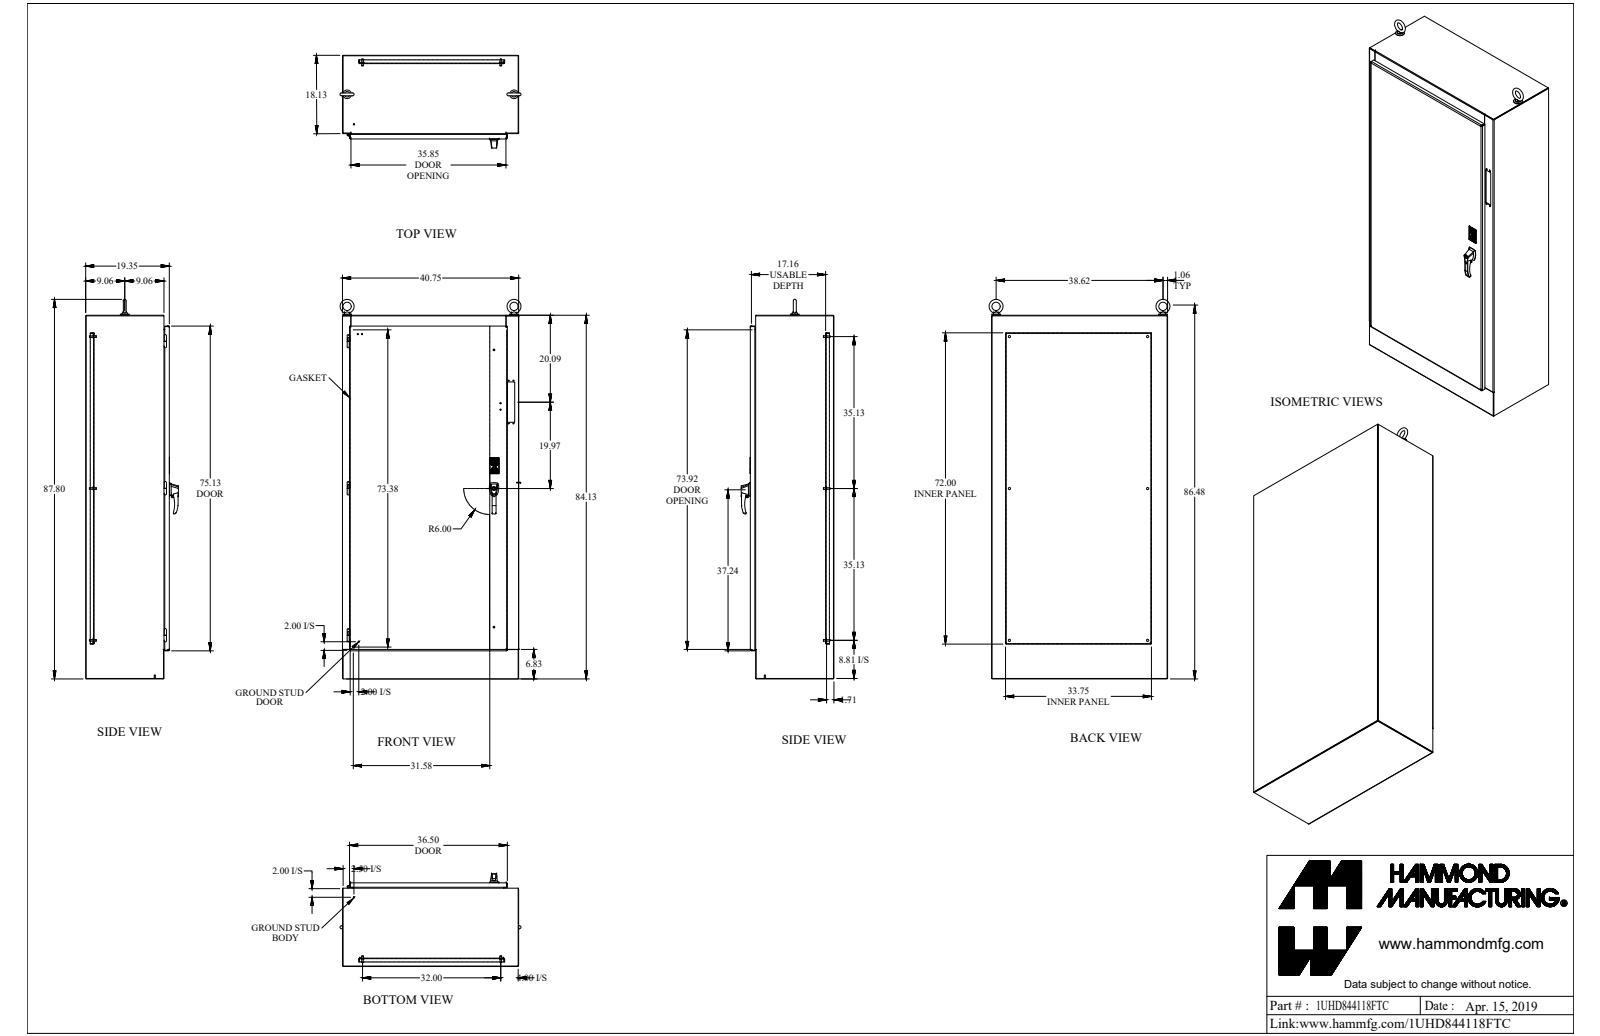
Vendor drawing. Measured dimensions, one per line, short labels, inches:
name: 1UHD844118FTC
written by: SolidWorks 2018 (AUTOMOTIVE_DESIGN)
unit: in
bodies: 102 solids, 1773 faces (978 planar, 482 cylindrical, 313 other)
size: 87.799 × 41.872 × 21.464
volume: 2 003 in³; area: 32 090 in²
holes: 7× ⌀0.307, 7× ⌀0.35, 6× ⌀0.281, 6× ⌀0.445, 6× ⌀0.563, 5× ⌀0.196, 3× ⌀0.25, 3× ⌀0.313, 2× ⌀0.167, 2× ⌀0.255, 2× ⌀0.257, 2× ⌀0.28
bosses: 10× ⌀0.25, 8× ⌀1, 7× ⌀0.375, 6× ⌀0.65, 6× ⌀0.33, 4× ⌀0.281, 4× ⌀0.188, 3× ⌀0.625
rounds: 31× R0.06, 30× R0.125, 25× R0.5, 20× R0.185, 16× R0.017, 13× R0.25, 12× R0.032, 8× R0.13
face distances: 0.125, 0.125, 17.413, 19.225, 19.1, 19.35, 19.224, 1.937, 1.812, 17.288
hole spacings: 32, 1, 1.125, 1.126, 1.287, 2, 7.5, 9.936
